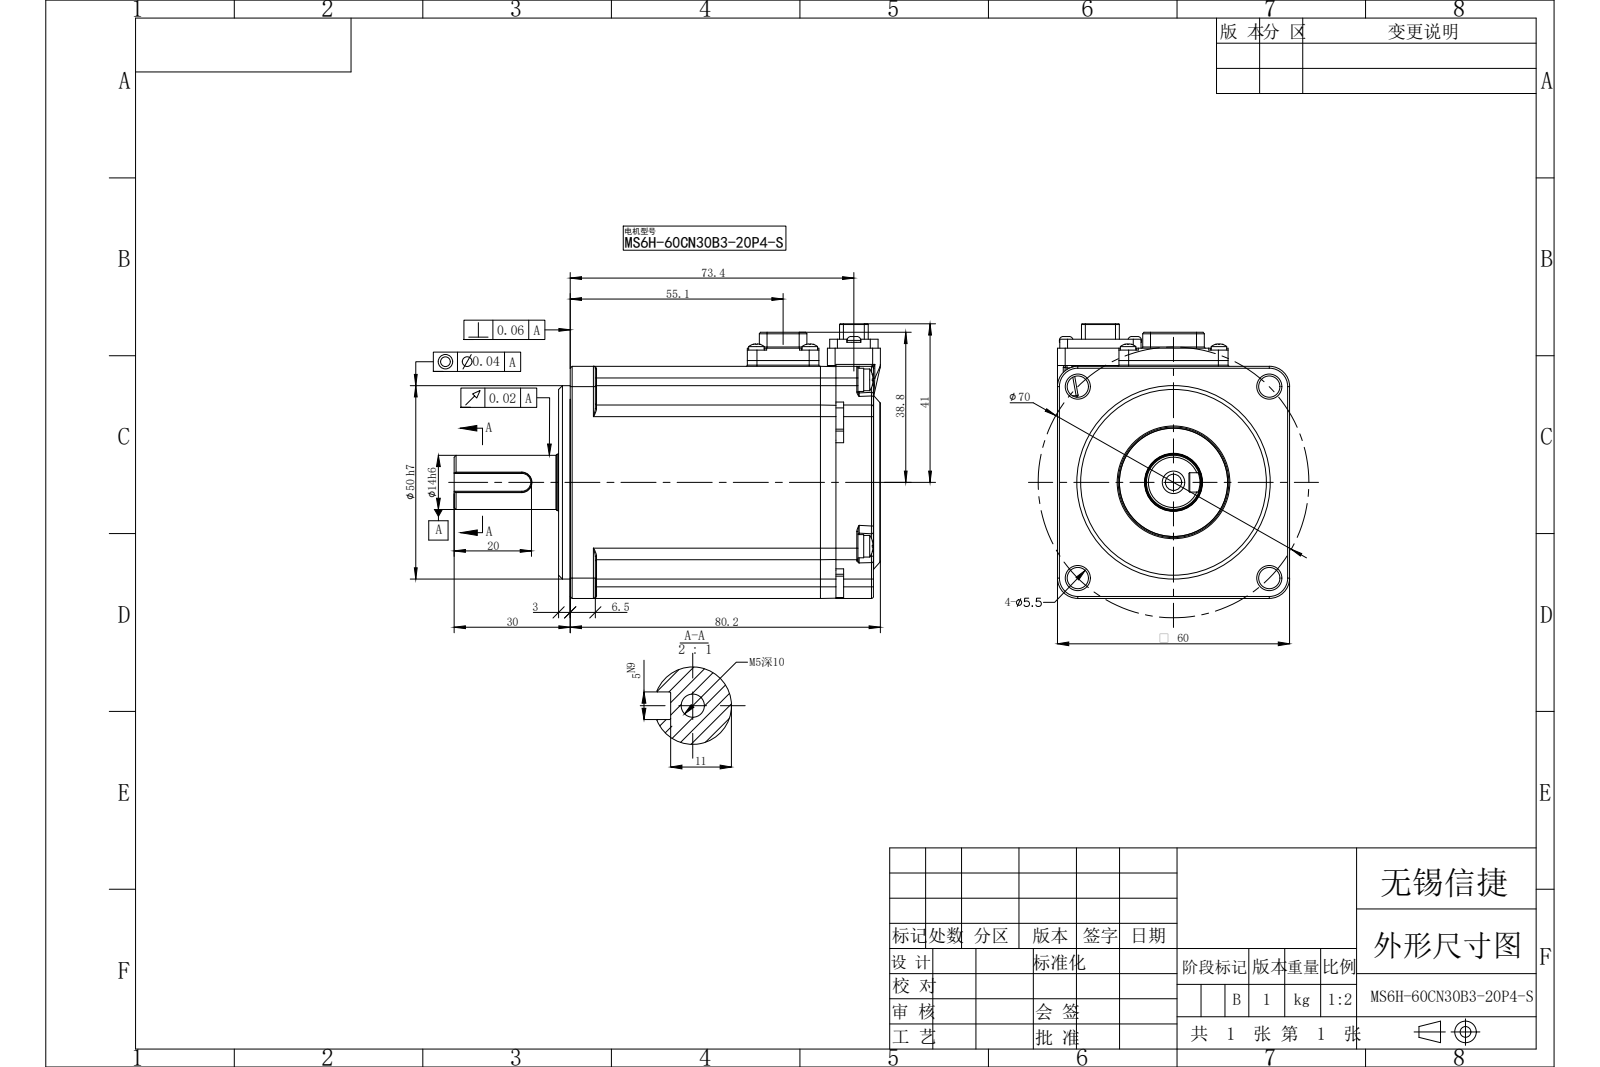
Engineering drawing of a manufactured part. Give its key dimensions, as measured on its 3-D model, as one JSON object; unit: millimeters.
{"part_name": "MS6H-60CN30B3-20P4-S", "step_written_by": "SolidWorks 2022 (CONFIG_CONTROL_DESIGN)", "units": "millimeters", "bodies": {"solids": 0, "faces": 734, "planar": 296, "cylindrical": 247, "other": 191}, "overall_size": [110.2, 71, 60], "round_holes": [[2.1, 8], [3.4, 4], [5.5, 4], [3.5, 3], [1.6, 2], [4.2, 1], [15, 1]], "round_bosses_or_shafts": [[3.5, 2], [50, 1], [28, 1], [14.8, 1], [14, 1]], "partial_cylinders_radius": [[0.5, 39], [0.3, 38], [0.2, 20], [3, 17], [2, 16], [1, 5], [2.5, 5], [0.6, 4]], "face_to_face_distances": [60, 71.7, 11.5, 83.2, 9.7, 3, 80.2, 68.7, 1.8, 78.4], "hole_center_spacings": [6.9, 8.43, 24.49, 31.22, 35, 41.29, 44.15, 49.5]}
